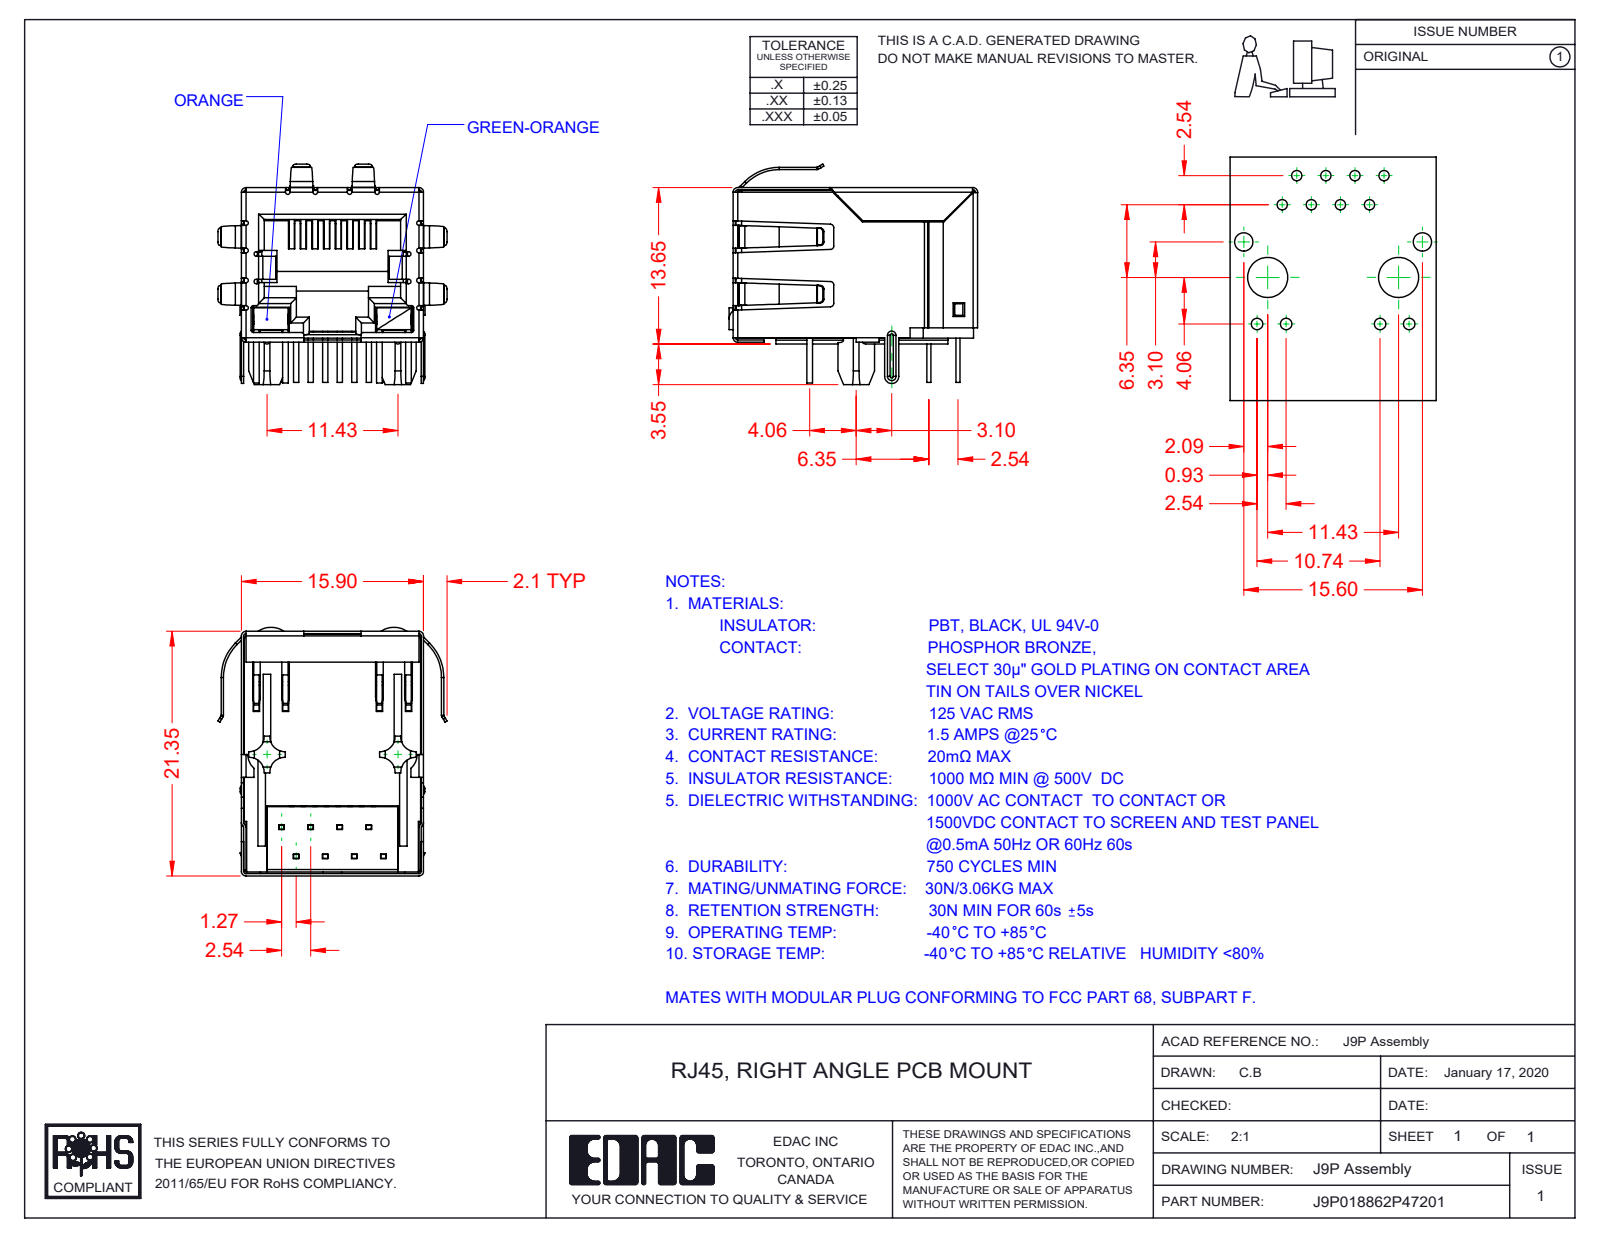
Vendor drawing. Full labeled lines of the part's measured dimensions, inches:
Part name (STEP PRODUCT): 9P-LED LED LH_4-Orange; 9P-LED Contacts; 9P-LED Assembly; 9P-LED Insulator (+4 more)
STEP written by: SolidWorks 2016 (CONFIG_CONTROL_DESIGN)
Units: inches
Bodies: 13 solids, 1474 faces (1042 planar, 338 cylindrical, 94 other)
Overall size (bounding box): 0.854 × 0.787 × 0.758
Volume: 0.164 in³ · Surface area: 11.65 in²
Partial cylindrical surfaces — rounded edges, fillets, slot ends (radius × count): R0.008 ×39, R0.02 ×22, R0.012 ×20, R0.016 ×16, R0.051 ×8, R0.009 ×5, R0.004 ×4, R0.012 ×4
Main face-to-face distances: 0.608, 0.618, 0.616, 0.014, 0.021, 0.61, 0.487, 0.024, 0.055, 0.023
